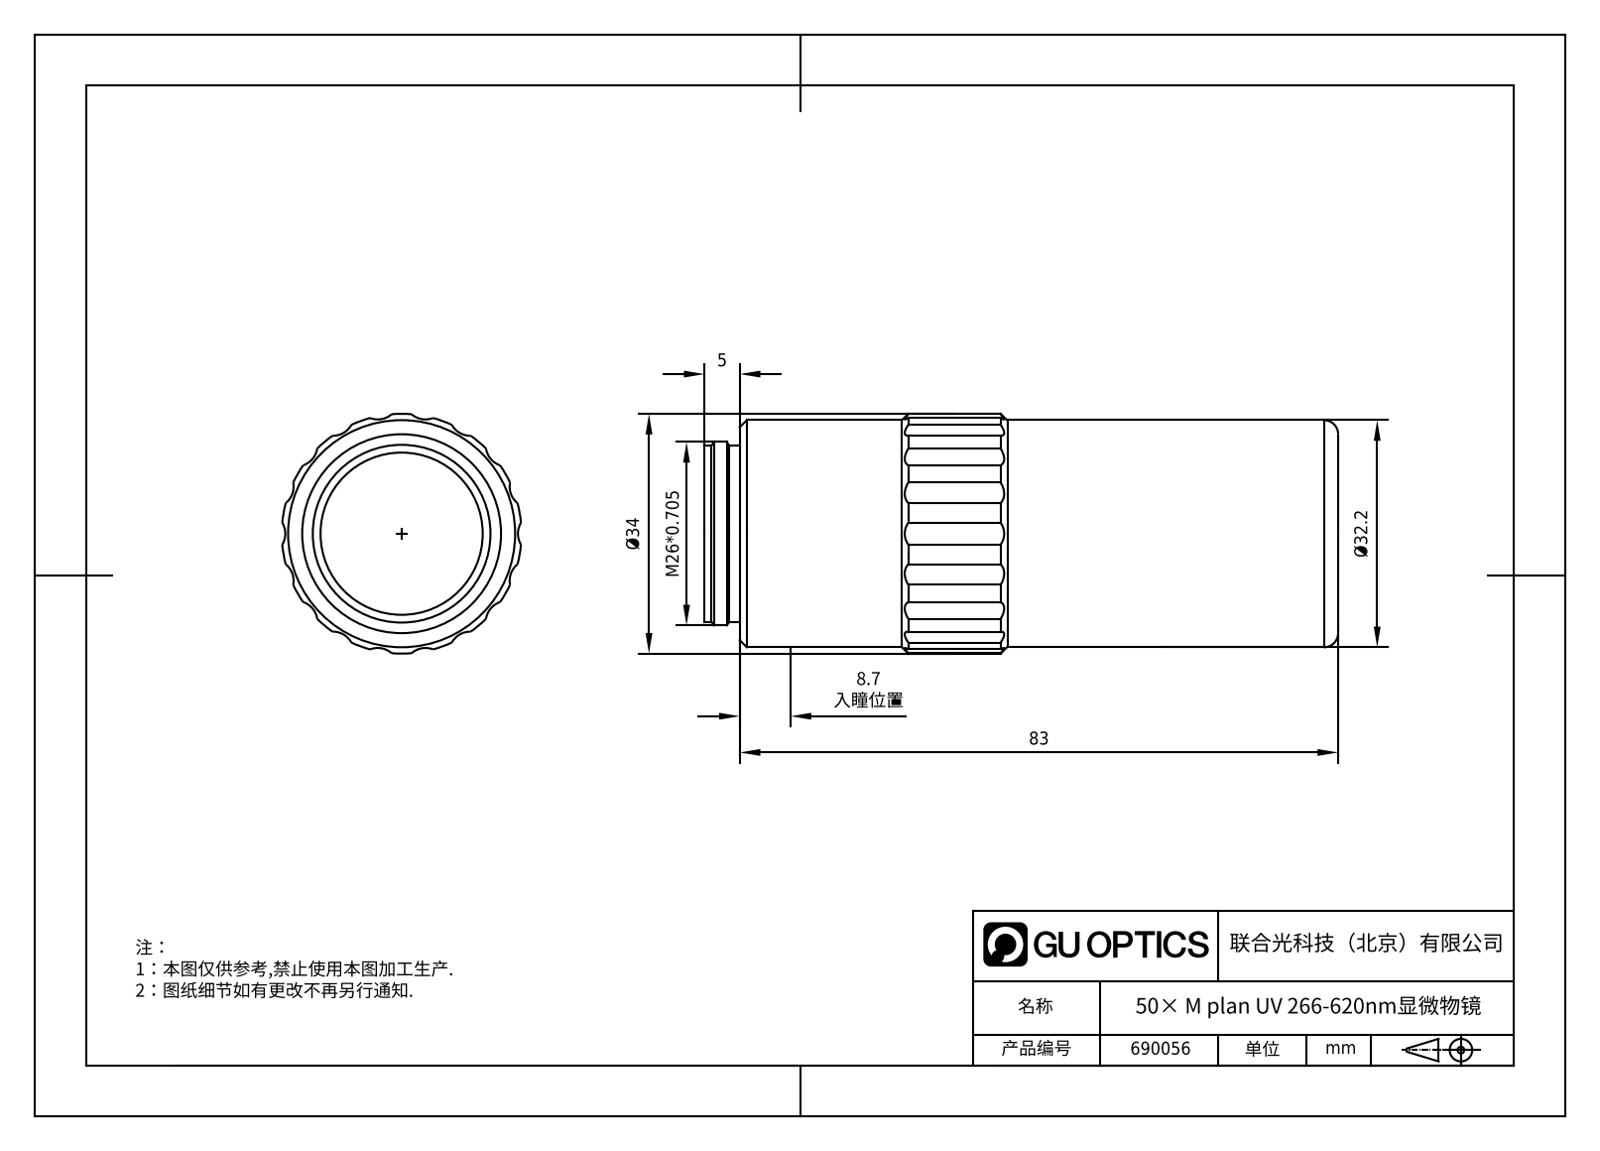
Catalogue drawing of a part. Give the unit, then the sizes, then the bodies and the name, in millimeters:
Units: millimetres
Overall size (bounding box): 88 × 34 × 33.86
Round holes (diameter × count): ⌀4.6 ×1, ⌀13 ×1
Round bosses / shafts (diameter × count): ⌀32.2 ×1, ⌀26 ×1, ⌀25 ×1
Partial cylindrical surfaces — rounded edges, fillets, slot ends (radius × count): R3 ×18, R17 ×1
Main face-to-face distances: 88, 5, 83, 1, 87, 82, 4, 86, 43, 42
Volume: 70 901 mm³ · Surface area: 10 564 mm²
Bodies: 1 solid, 55 faces (6 planar, 43 cylindrical, 6 other)
Part name (STEP PRODUCT): 690056
STEP written by: SolidWorks 2020 (CONFIG_CONTROL_DESIGN)
